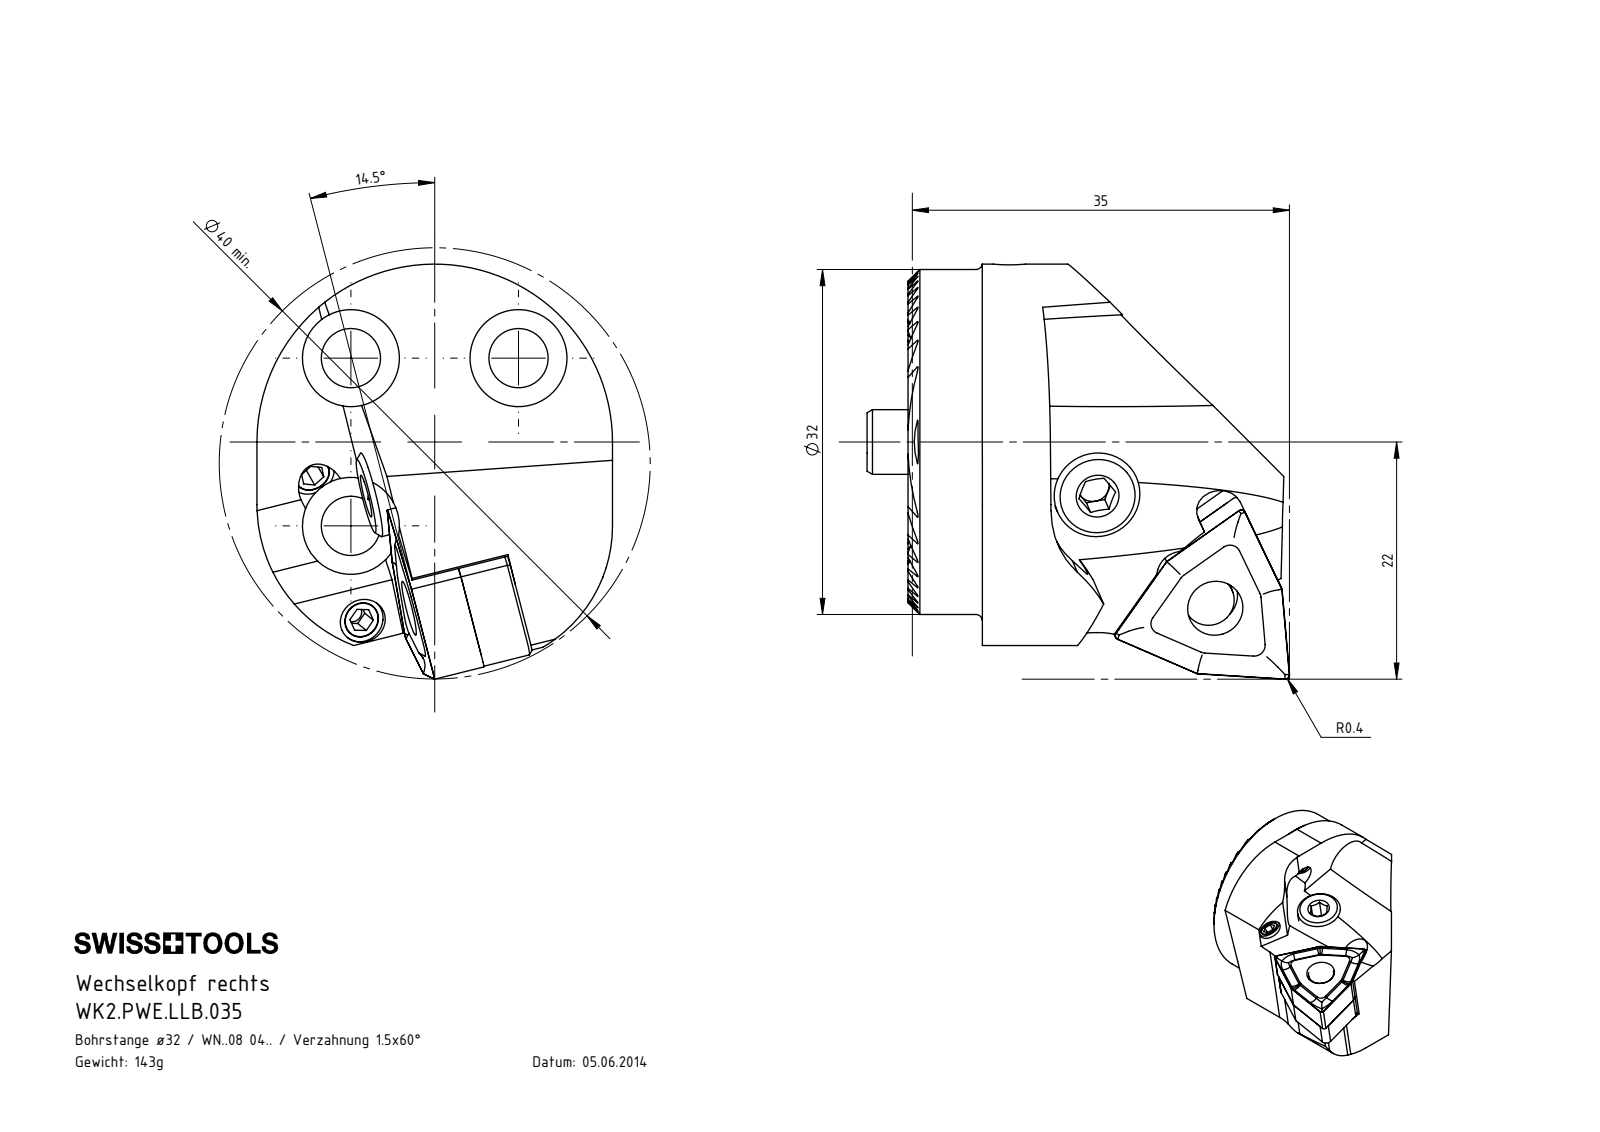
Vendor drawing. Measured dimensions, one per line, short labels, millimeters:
name: KVT_MB_600_030; WWE-ER2.101.004_A; WCD-ER4.101.017_A; WK2-PWE.LLB.035_B (+6 more)
written by: SolidWorks 2017 (AUTOMOTIVE_DESIGN)
unit: mm
bodies: 15 solids, 657 faces (253 planar, 212 cylindrical, 192 other)
size: 39.21 × 38.51 × 33
volume: 17 595 mm³; area: 11 354 mm²
holes: 3× ⌀2.38, 3× ⌀2.5, 3× ⌀4.2, 3× ⌀5.5, 3× ⌀9, 2× ⌀1.7, 2× ⌀3, 2× ⌀3.3, 1× ⌀5.16, 1× ⌀6.7, 1× ⌀7, 1× ⌀7.8
bosses: 3× ⌀3, 2× ⌀4, 1× ⌀32, 1× ⌀8, 1× ⌀7.9, 1× ⌀6.4, 1× ⌀6, 1× ⌀4.7
rounds: 22× R0.12, 4× R2.5, 3× R0.4, 3× R1, 2× R3.2, 2× R7, 1× R2.1, 1× R2.3
face distances: 1.3, 2.6, 3.9, 5.2, 6.5, 12.99, 11.69, 14.29, 7.8, 10.39
hole spacings: 11, 15.56, 15.59, 22.01
